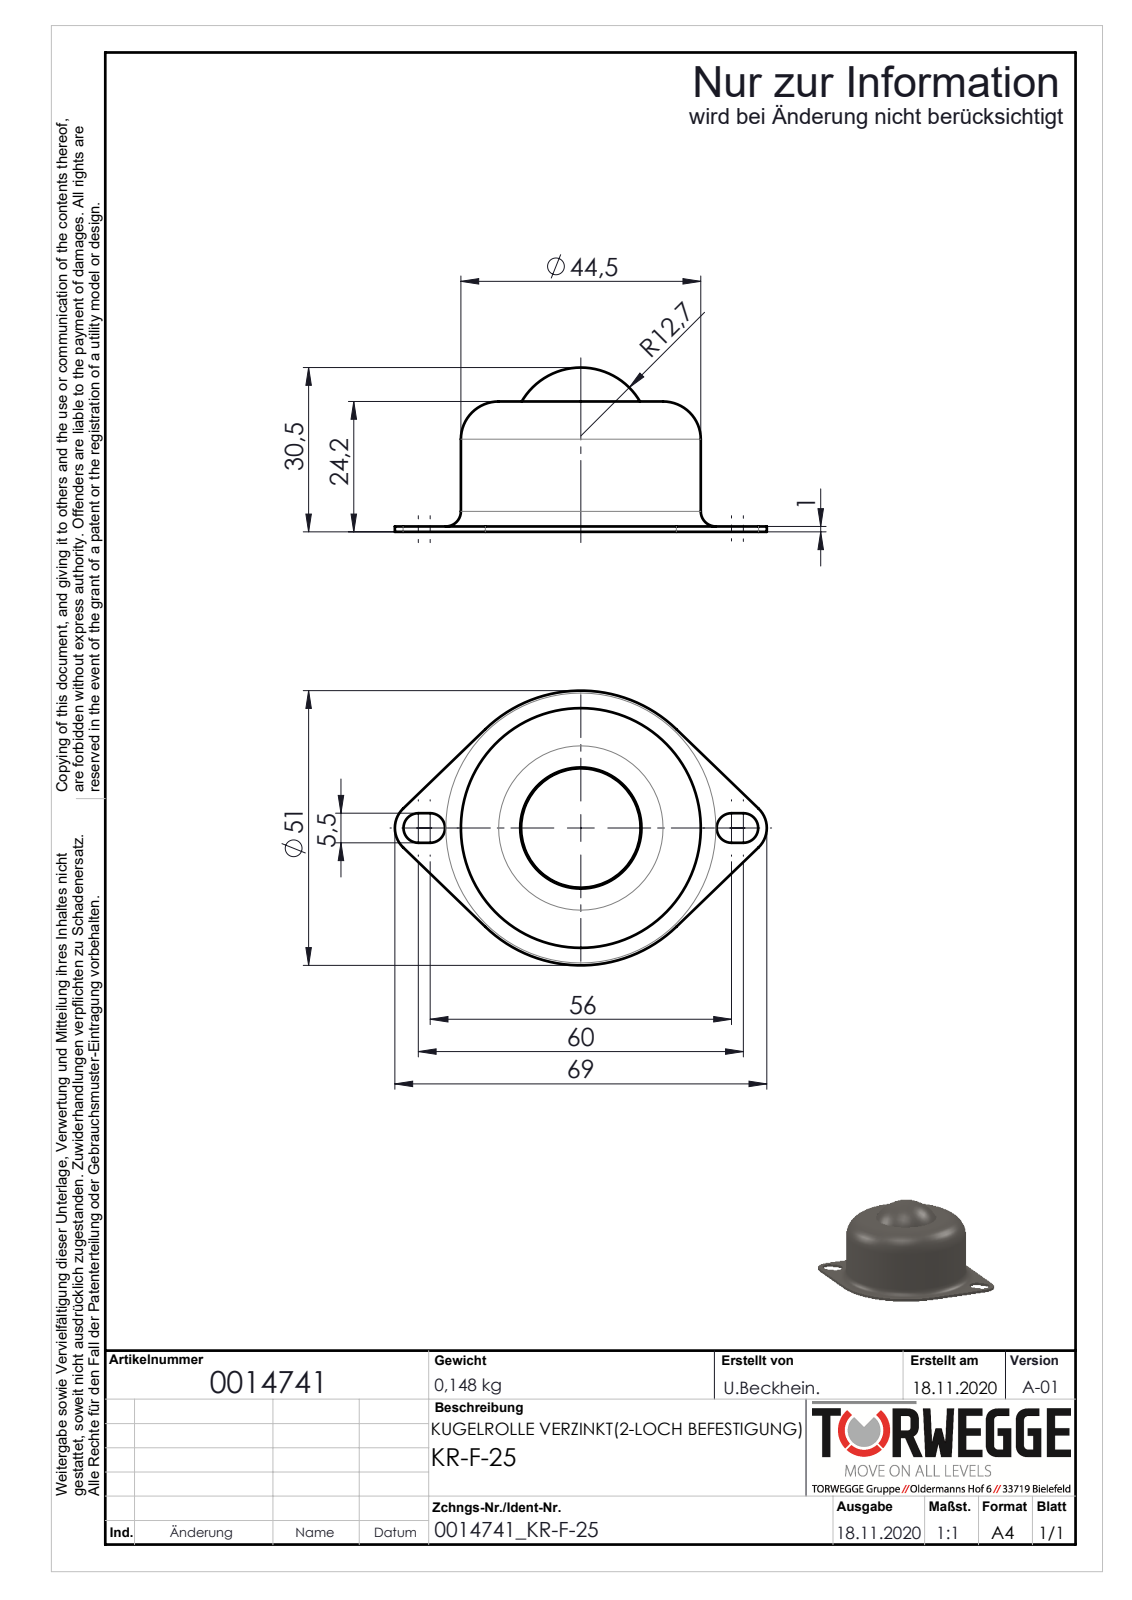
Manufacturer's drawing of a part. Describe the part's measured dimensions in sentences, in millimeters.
The part is named "0014741". Its 3-D file was written by "SolidWorks 2018 (AUTOMOTIVE_DESIGN)". It is 1 solid with 53 faces: 16 planar, 23 cylindrical and 14 other. Overall it measures 69 by 51 by 30.32 millimeters. Its volume is 32 293 cubic millimeters and its surface area 10 052 square millimeters. Round holes: 1 of diameter 2, 1 of diameter 9.5, 1 of diameter 22.5, 1 of diameter 41.6, 1 of diameter 43.4. Round bosses or shafts: 1 of diameter 44.5, 1 of diameter 35. Partial cylindrical surfaces (rounded edges, fillets, slot ends): 4 of radius 2.75, 2 of radius 5, 1 of radius 25.5. The main face-to-face distances are 24.2, 1, 23.2, 8.9, 7.9, 15.3, 51, 11.95, 10.95, 3.05.
